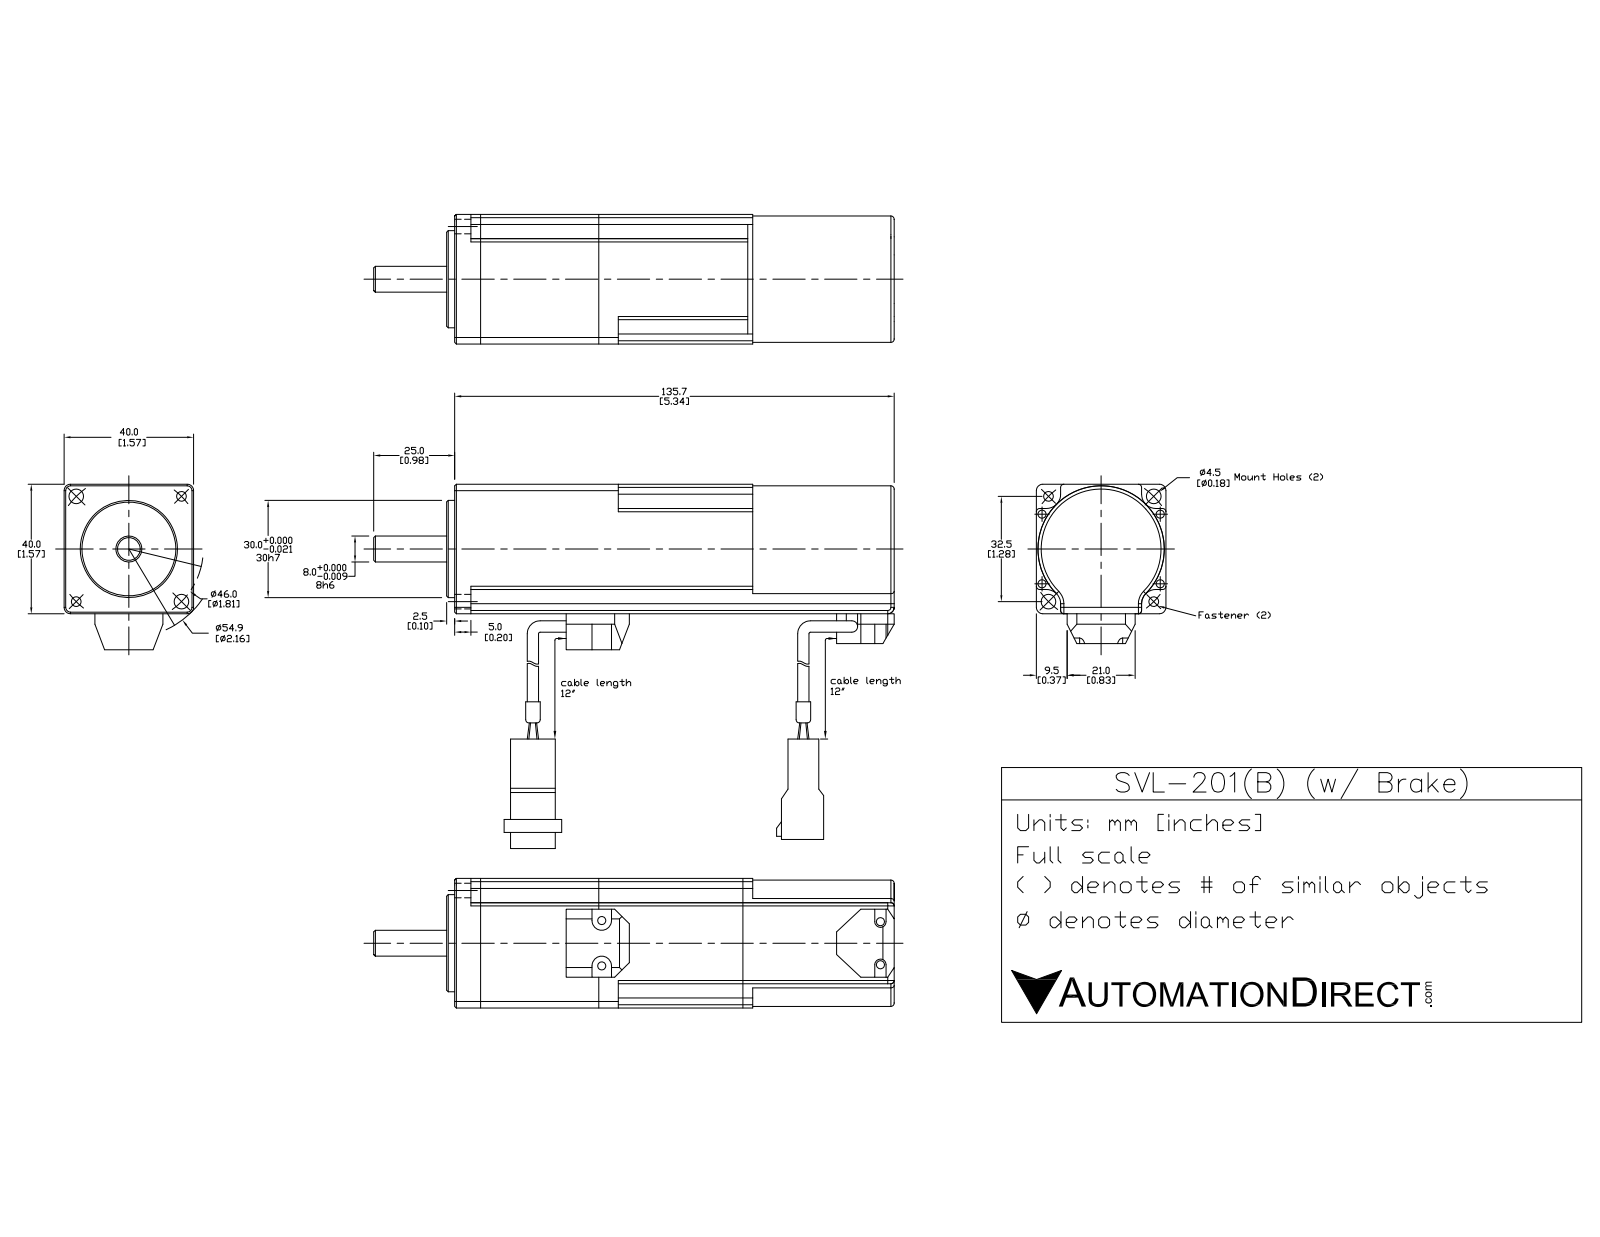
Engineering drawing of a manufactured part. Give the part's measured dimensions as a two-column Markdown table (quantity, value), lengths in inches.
| quantity | value |
| --- | --- |
| part name | SVL-201B |
| STEP written by | SolidWorks 2015 (AUTOMOTIVE_DESIGN) |
| units | inches |
| bodies | 12 solids, 296 faces (165 planar, 106 cylindrical, 25 other) |
| overall size | 6.398 × 2.102 × 1.959 |
| volume | 12.28 in³ |
| surface area | 57.62 in² |
| round holes (diameter × count) | 0.098 × 2, 0.177 × 2, 0.512 × 1 |
| round bosses / shafts (diameter × count) | 0.197 × 4, 0.217 × 3, 1.181 × 1, 0.315 × 1, 0.276 × 1 |
| partial cylindrical surfaces (radius × count) | 0.079 × 17, 0.039 × 16, 0.098 × 4, 0.108 × 4, 0.173 × 4, 0.768 × 1 |
| main face-to-face distances | 1.575, 1.437, 1.811, 3.248, 3.661, 1.85, 5.098, 0.295, 5.413, 3.563 |
| hole center spacings | 0.906, 1.28, 1.811 |
